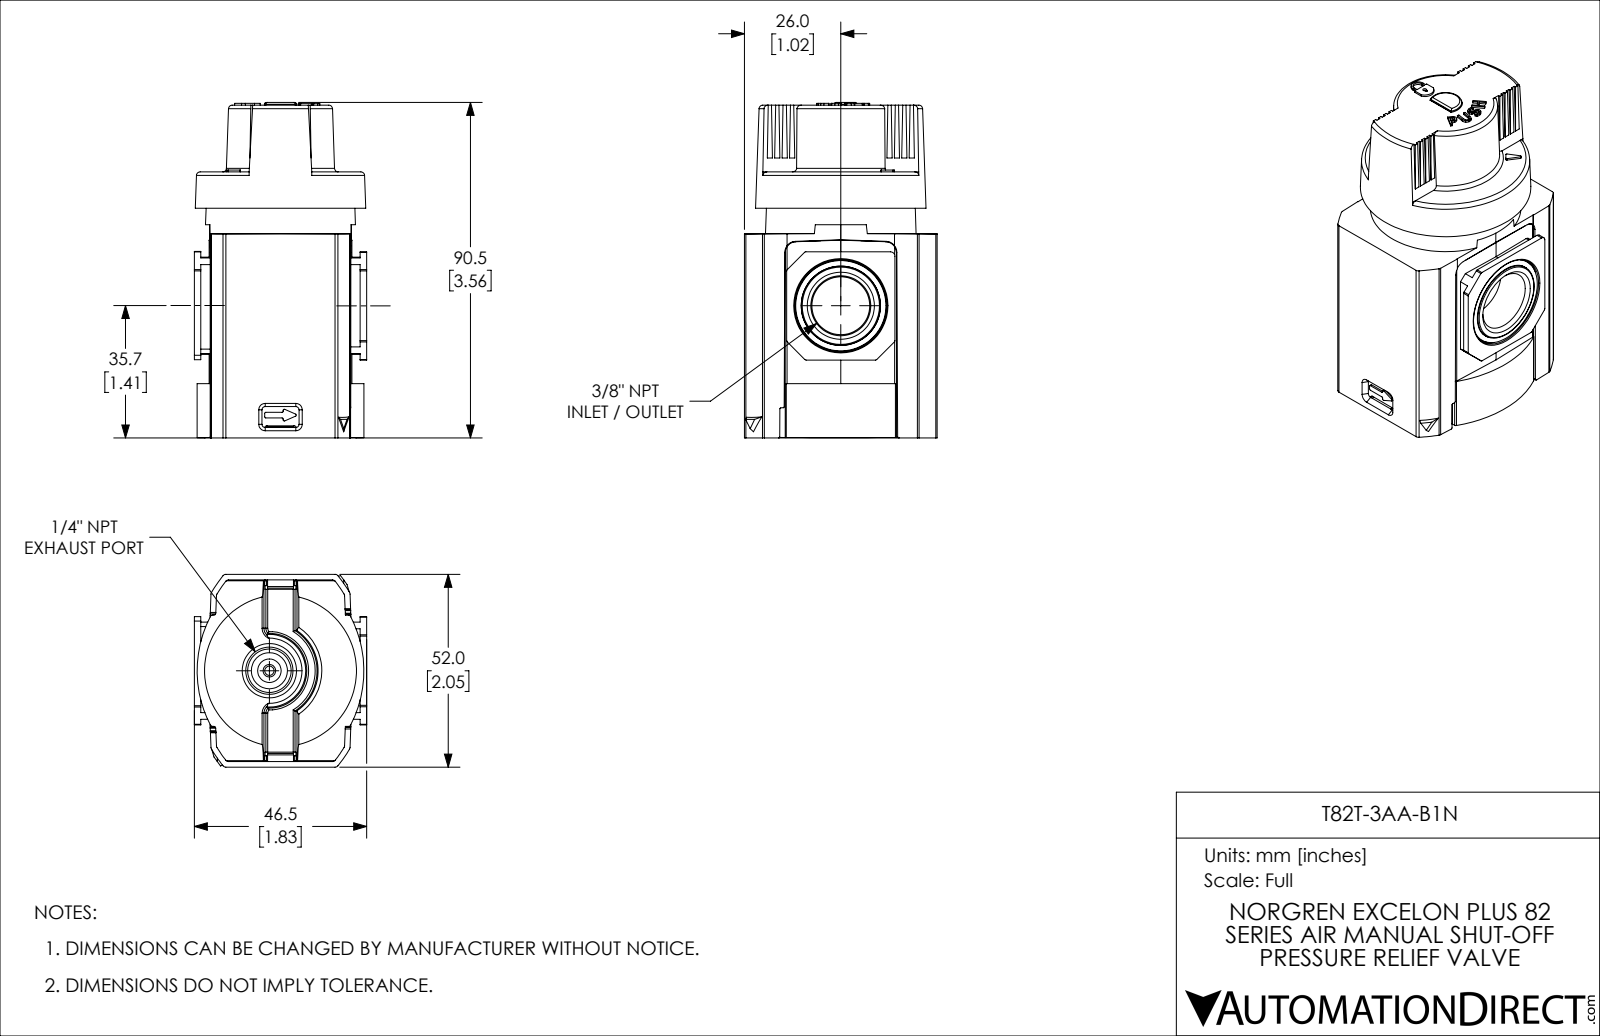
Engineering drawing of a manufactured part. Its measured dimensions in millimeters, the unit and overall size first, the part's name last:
Units: millimetres
Overall size (bounding box): 90.5 × 52 × 46.5
Round holes (diameter × count): ⌀1 ×1, ⌀5.1 ×1
Round bosses / shafts (diameter × count): ⌀29.8 ×1, ⌀20.5 ×1, ⌀19.8 ×1, ⌀19.5 ×1, ⌀6 ×1
Partial cylindrical surfaces — rounded edges, fillets, slot ends (radius × count): R0.5 ×41, R1 ×34, R0.3 ×13, R3 ×8, R0.3 ×7, R1.2 ×4, R0.1 ×2, R0.4 ×2
Main face-to-face distances: 1.5, 50.5, 52, 49, 29.7, 4.6, 34.3, 3.1, 32.8, 37.5
Volume: 95 770 mm³ · Surface area: 46 150 mm²
Bodies: 3 solids, 804 faces (382 planar, 245 cylindrical, 177 other)
Part name (STEP PRODUCT): T82T-3AA-B1N
STEP written by: SolidWorks 2021 (CONFIG_CONTROL_DESIGN)
